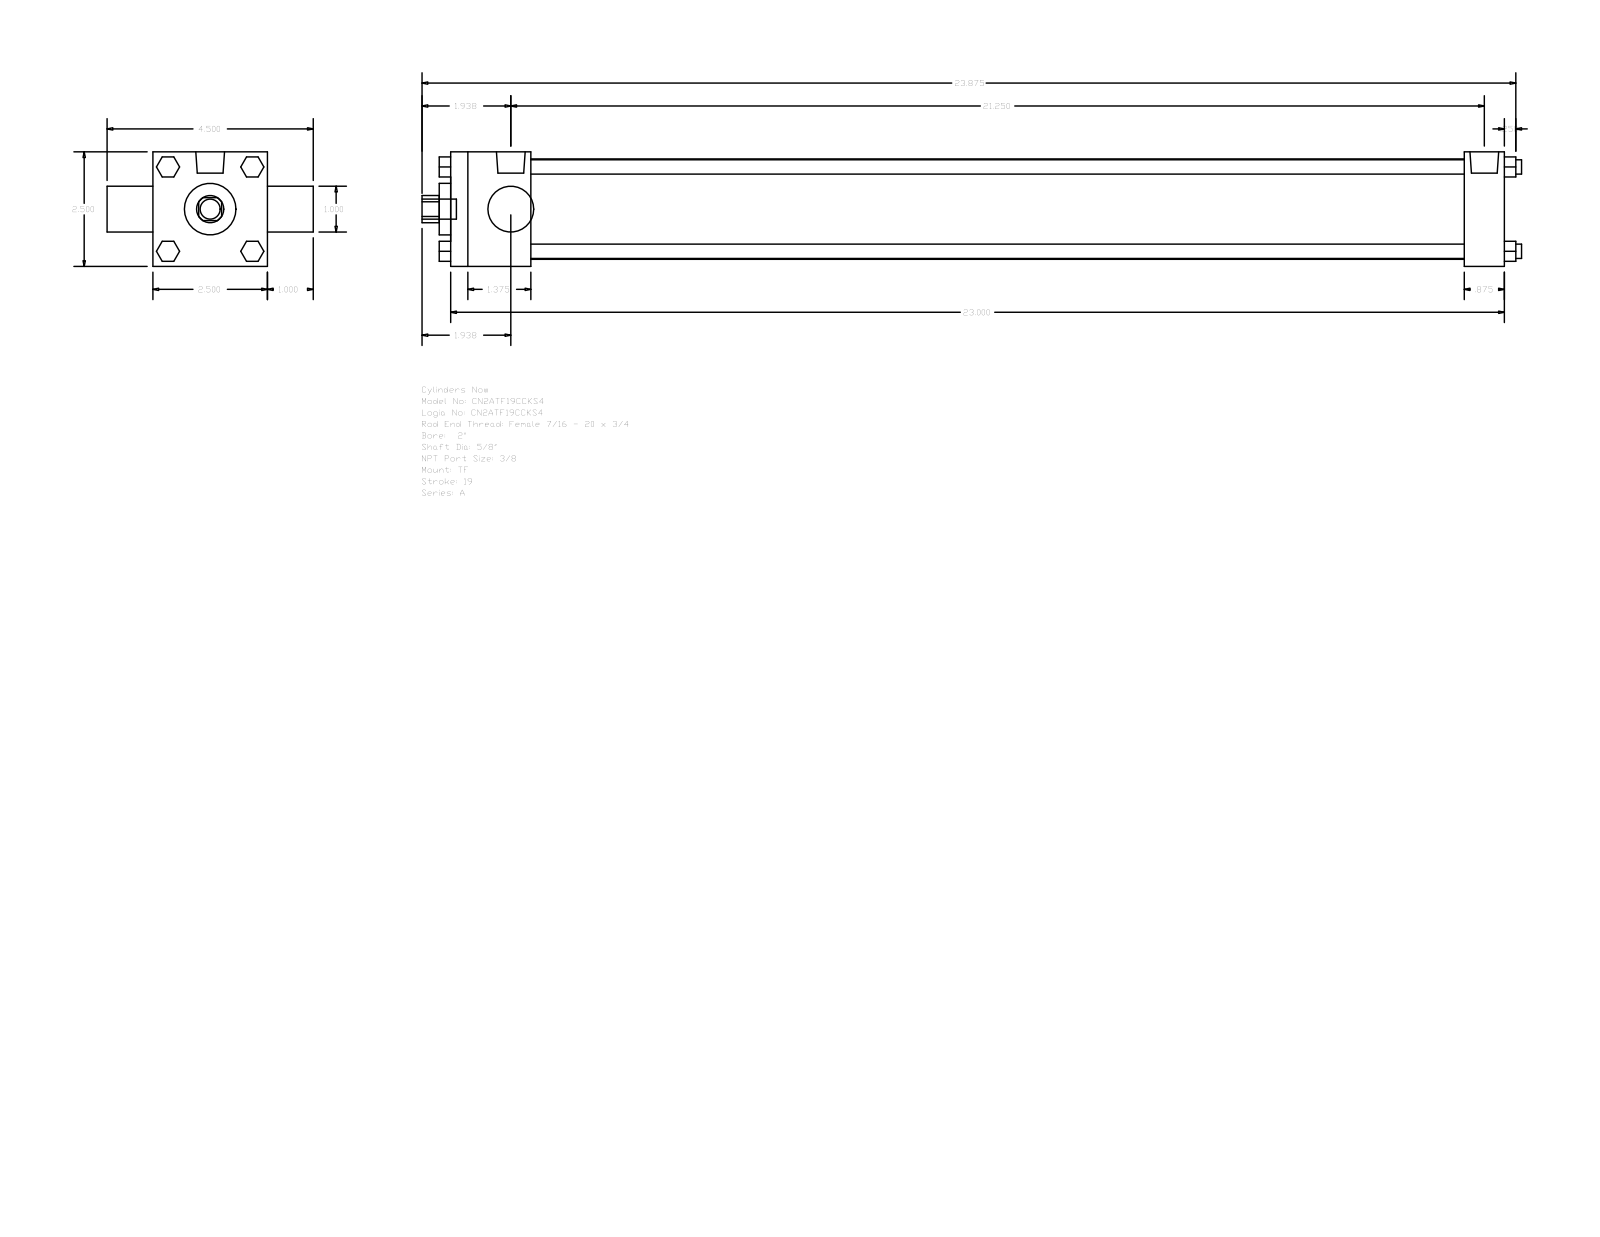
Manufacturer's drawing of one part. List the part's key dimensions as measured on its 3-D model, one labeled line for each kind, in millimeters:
Part name (STEP PRODUCT): A_TF__0200_0.625
STEP written by: GSSL Pune (CONFIG_CONTROL_DESIGN)
Units: millimetres
Bodies: 0 solids, 120 faces (92 planar, 28 cylindrical, 0 other)
Overall size (bounding box): 609.6 × 114.3 × 63.5
Round holes (diameter × count): ⌀15.88 ×1, ⌀25.4 ×1, ⌀28.57 ×1, ⌀55.63 ×1
Round bosses / shafts (diameter × count): ⌀7.94 ×4, ⌀5.56 ×3, ⌀15.93 ×2, ⌀11.11 ×1
Partial cylindrical surfaces — rounded edges, fillets, slot ends (radius × count): R7.54 ×1
Main face-to-face distances: 63.5, 584.2, 44.45, 561.97, 517.52, 539.75, 22.23, 25.4, 88.9, 50.8
